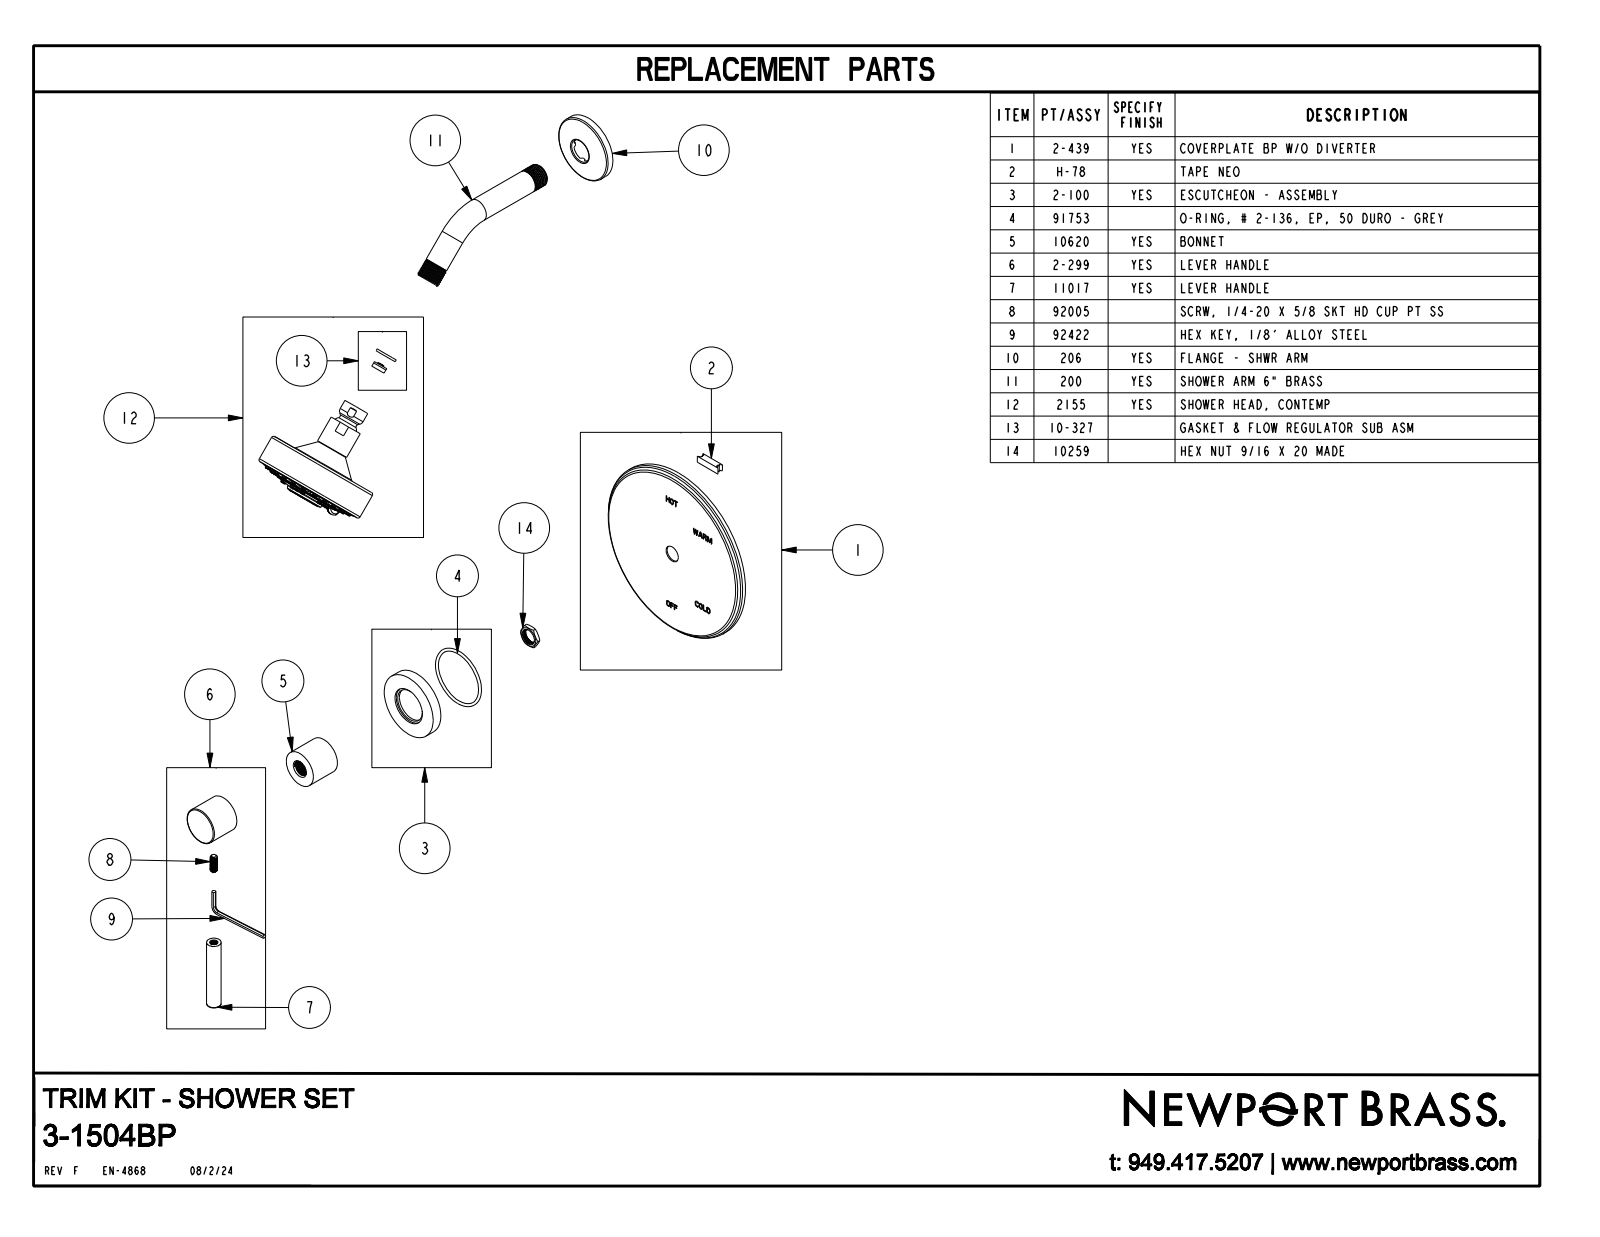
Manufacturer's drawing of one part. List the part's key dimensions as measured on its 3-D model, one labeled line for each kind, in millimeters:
Part name (STEP PRODUCT): 3-1504BP
STEP written by: CREO PARAMETRIC BY PTC INC, 2018400 (CONFIG_CONTROL_DESIGN)
Units: millimetres
Bodies: 2 solids, 1401 faces (466 planar, 204 cylindrical, 731 other)
Overall size (bounding box): 417.6 × 207.6 × 165.1
Volume: 587 000 mm³ · Surface area: 105 300 mm²
Round holes (diameter × count): ⌀1.5 ×8, ⌀13.2 ×1, ⌀23.5 ×1
Round bosses / shafts (diameter × count): ⌀3.6 ×39, ⌀4.2 ×23, ⌀20.7 ×2, ⌀165.1 ×1, ⌀101.6 ×1, ⌀94.6 ×1, ⌀60.5 ×1, ⌀60.3 ×1
Partial cylindrical surfaces — rounded edges, fillets, slot ends (radius × count): R2 ×8, R0.5 ×2, R3.5 ×1, R12 ×1, R13 ×1, R16 ×1
Main face-to-face distances: 8, 17.5, 9.5, 0.5, 38.2, 74.6, 66.6, 57.1, 45.6, 37.7
Hole centre spacings: 11.3, 14.7, 20.8, 20.8, 27.2, 11.3, 14.7, 27.2
